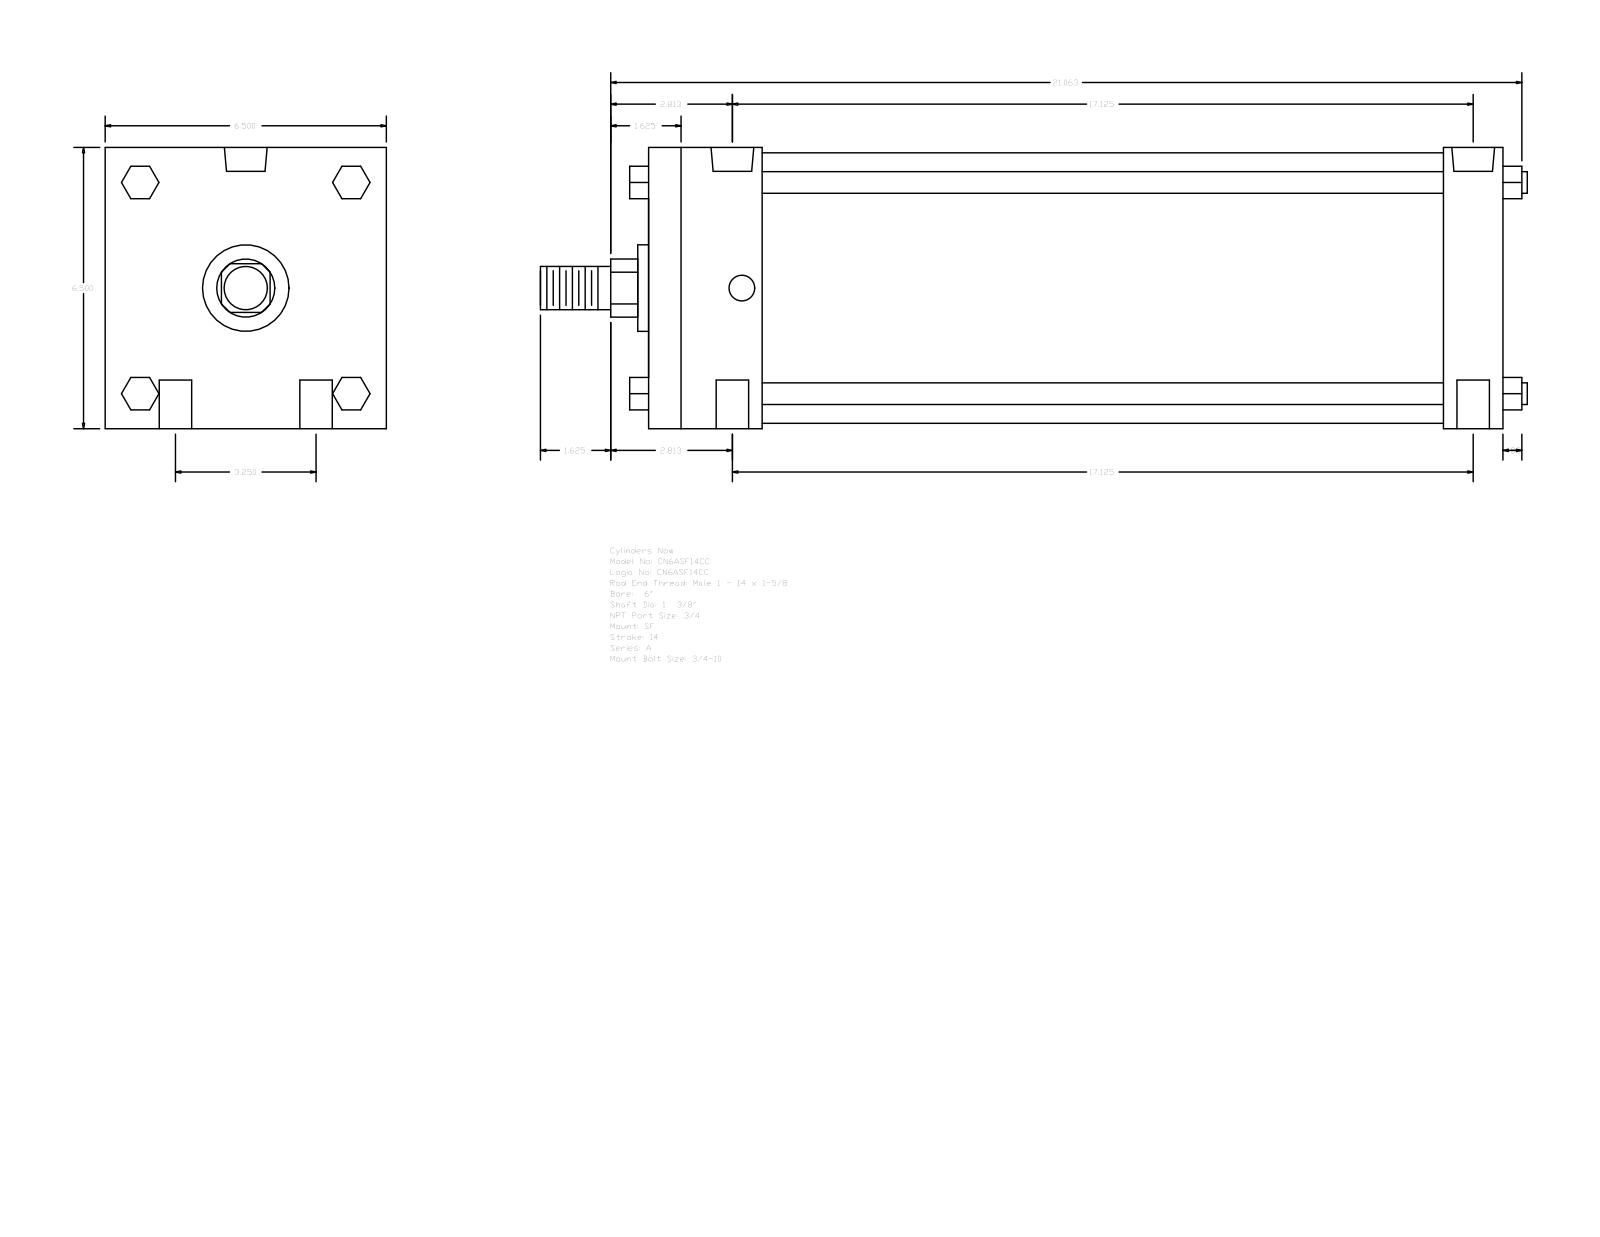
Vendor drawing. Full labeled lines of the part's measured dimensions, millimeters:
Part name (STEP PRODUCT): A_SF__0600_1.375
STEP written by: GSSL Pune (CONFIG_CONTROL_DESIGN)
Units: millimetres
Bodies: 0 solids, 124 faces (94 planar, 30 cylindrical, 0 other)
Overall size (bounding box): 579.44 × 165.1 × 165.1
Round holes (diameter × count): ⌀19.05 ×4, ⌀15.08 ×2, ⌀25.12 ×2
Round bosses / shafts (diameter × count): ⌀12.7 ×4, ⌀158.75 ×1, ⌀50.8 ×1, ⌀34.92 ×1, ⌀25.4 ×1
Partial cylindrical surfaces — rounded edges, fillets, slot ends (radius × count): R17.06 ×1
Main face-to-face distances: 165.1, 501.65, 466.72, 34.93, 66.67, 400.05, 434.98, 19.05, 61.97, 107.34
Hole centre spacings: 41.27, 436.92, 434.97, 82.54, 442.73, 423.85
